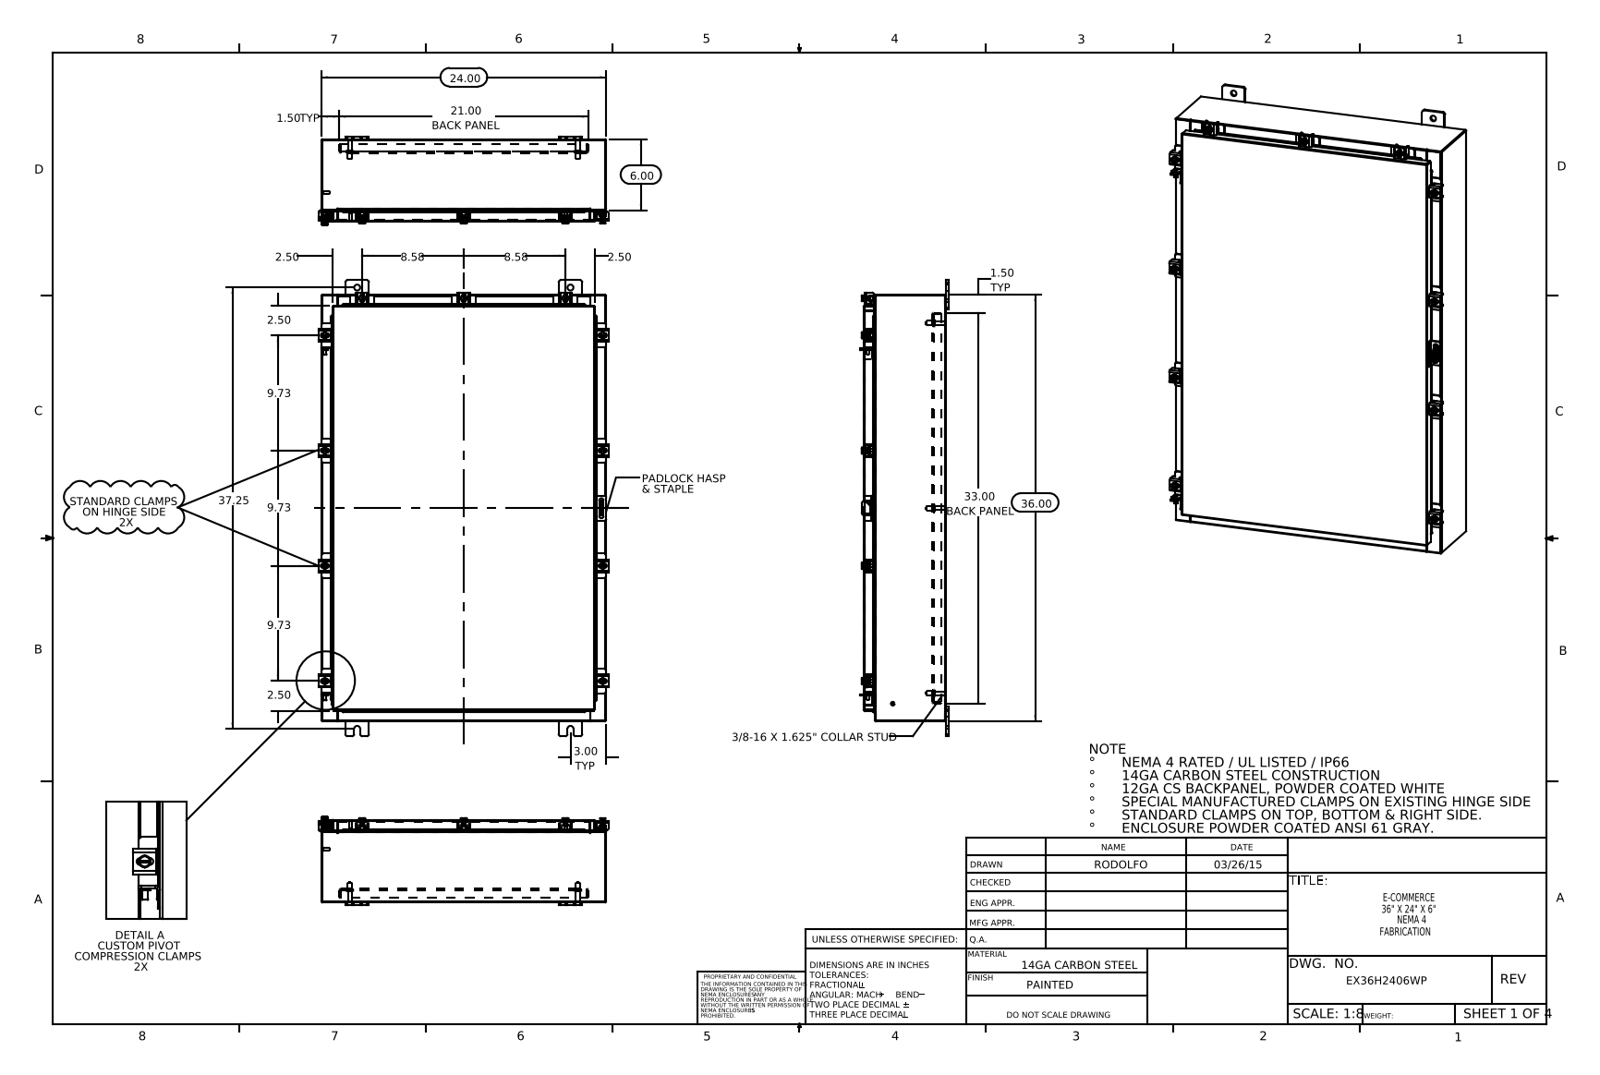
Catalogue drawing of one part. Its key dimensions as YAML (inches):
part_name: "Clamp Top_RTP31; EX36H2406WP Cover; EX36H2406WP Bottom; EX36H2406WP Backpanel (+8 more)"
step_written_by: "SolidWorks 2014 (CONFIG_CONTROL_DESIGN)"
units: inches
bodies: {solids: 78, faces: 1971, planar: 1041, cylindrical: 758, other: 172}
overall_size: [38.5, 24.421, 7.453]
volume: 290.3
surface_area: 7154
round_holes:
  - {diameter: 0.213, count: 11}
  - {diameter: 0.26, count: 11}
  - {diameter: 0.5, count: 10}
  - {diameter: 0.125, count: 1}
  - {diameter: 0.25, count: 1}
round_bosses_or_shafts:
  - {diameter: 0.5, count: 11}
  - {diameter: 0.25, count: 11}
  - {diameter: 0.399, count: 9}
  - {diameter: 0.625, count: 6}
  - {diameter: 0.375, count: 6}
  - {diameter: 0.33, count: 6}
  - {diameter: 0.315, count: 2}
  - {diameter: 0.236, count: 2}
partial_cylinders:
  - {radius: 0.06, count: 48}
  - {radius: 0.013, count: 26}
  - {radius: 0.19, count: 24}
  - {radius: 0.088, count: 22}
  - {radius: 0.141, count: 22}
  - {radius: 0.09, count: 20}
  - {radius: 0.12, count: 20}
  - {radius: 0.05, count: 19}
face_to_face_distances: [0.075, 6.9, 6.975, 6.826, 0.104, 1, 1.075, 5.826, 5.9, 1.179]
hole_center_spacings: [25.389, 5.299, 9.73, 10.964, 14.744, 15.625, 19.459, 20.597]
